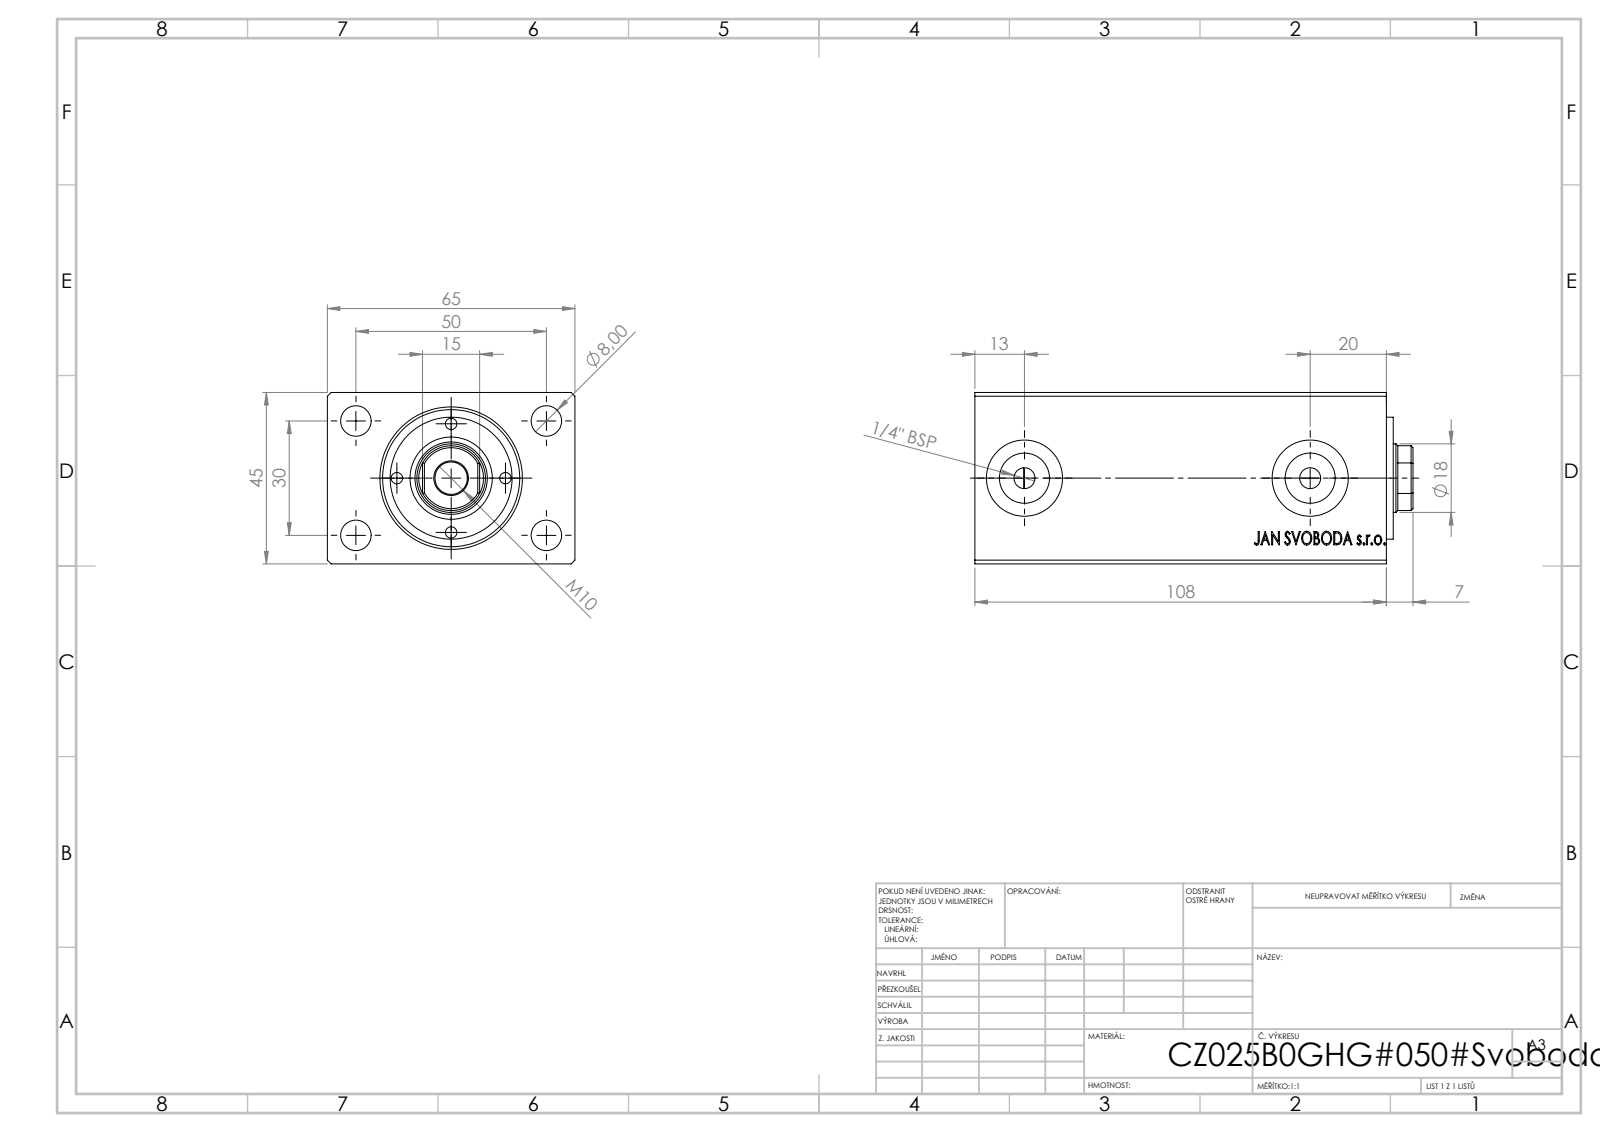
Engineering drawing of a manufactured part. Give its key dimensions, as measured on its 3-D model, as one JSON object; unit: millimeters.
{"part_name": "V500CZ; V500CZ_B_VC", "step_written_by": "SolidWorks 2019 (CONFIG_CONTROL_DESIGN)", "units": "millimeters", "bodies": {"solids": 3, "faces": 873, "planar": 399, "cylindrical": 58, "other": 416}, "overall_size": [115, 65, 45], "volume_mm3": 289605, "surface_area_mm2": 54124, "round_holes": [[3, 4], [8, 4], [5.5, 2], [13.16, 2], [20, 2], [8.5, 1], [18, 1], [19, 1], [25, 1], [36, 1]], "round_bosses_or_shafts": [[32, 1]], "partial_cylinders_radius": [[8.5, 1]], "face_to_face_distances": [45, 65, 108, 7, 107.8, 95.2, 12.6, 12.8, 1.8, 5.2], "hole_center_spacings": [14.25, 18.45, 20.15, 25.01, 29.15, 38.48, 42.02, 28.5]}
